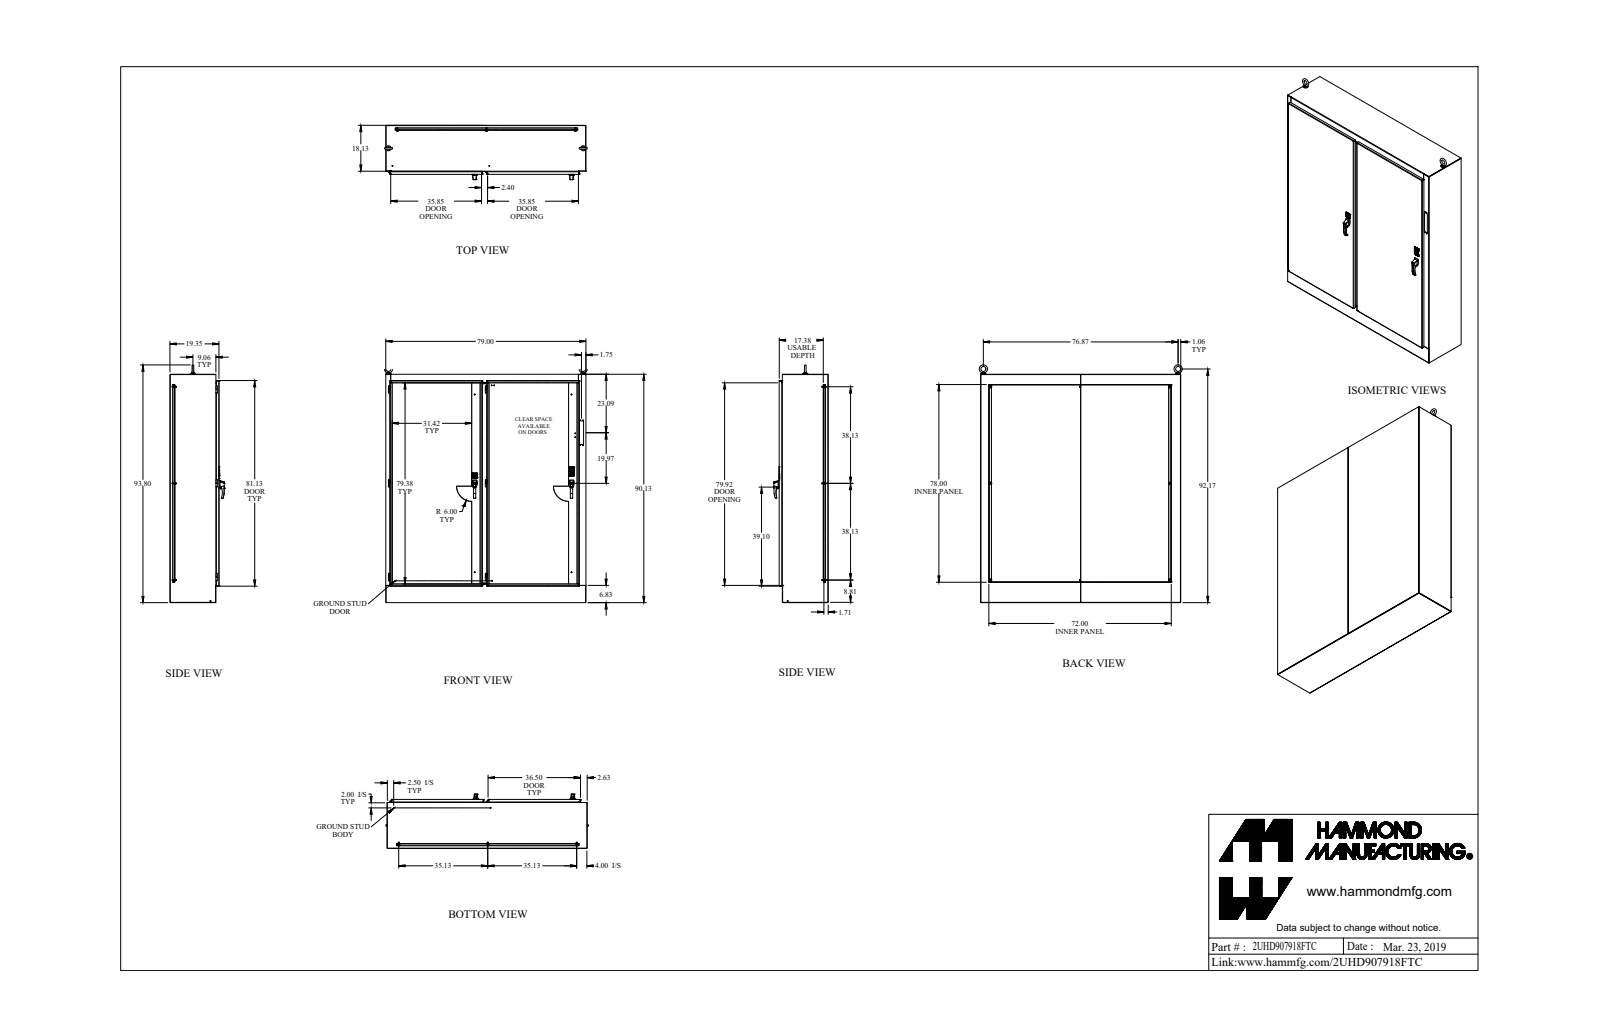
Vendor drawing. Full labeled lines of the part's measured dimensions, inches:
Part name (STEP PRODUCT): 2UHD907918FTC
STEP written by: SolidWorks 2018 (AUTOMOTIVE_DESIGN)
Units: inches
Bodies: 217 solids, 3088 faces (1806 planar, 908 cylindrical, 374 other)
Overall size (bounding box): 93.799 × 80.122 × 21.466
Volume: 5 931 in³ · Surface area: 61 566 in²
Round holes (diameter × count): ⌀0.196 ×12, ⌀0.281 ×11, ⌀0.307 ×11, ⌀0.25 ×10, ⌀0.35 ×8, ⌀0.257 ×6, ⌀0.313 ×6, ⌀0.445 ×5, ⌀0.28 ×4, ⌀0.282 ×4, ⌀0.375 ×4, ⌀0.39 ×4
Round bosses / shafts (diameter × count): ⌀0.25 ×19, ⌀1 ×12, ⌀0.65 ×9, ⌀0.375 ×9, ⌀0.33 ×9, ⌀0.281 ×8, ⌀0.75 ×6, ⌀0.53 ×6
Partial cylindrical surfaces — rounded edges, fillets, slot ends (radius × count): R0.125 ×62, R0.06 ×55, R0.5 ×42, R0.185 ×34, R0.03 ×28, R0.017 ×16, R0.018 ×16, R0.032 ×12
Main face-to-face distances: 0.125, 0.072, 17.431, 19.369, 19.243, 1.937, 1.812, 1.865, 1.74, 17.503
Hole centre spacings: 38.249, 1, 1.126, 1.287, 33.937, 35.063, 35.068, 36.188
